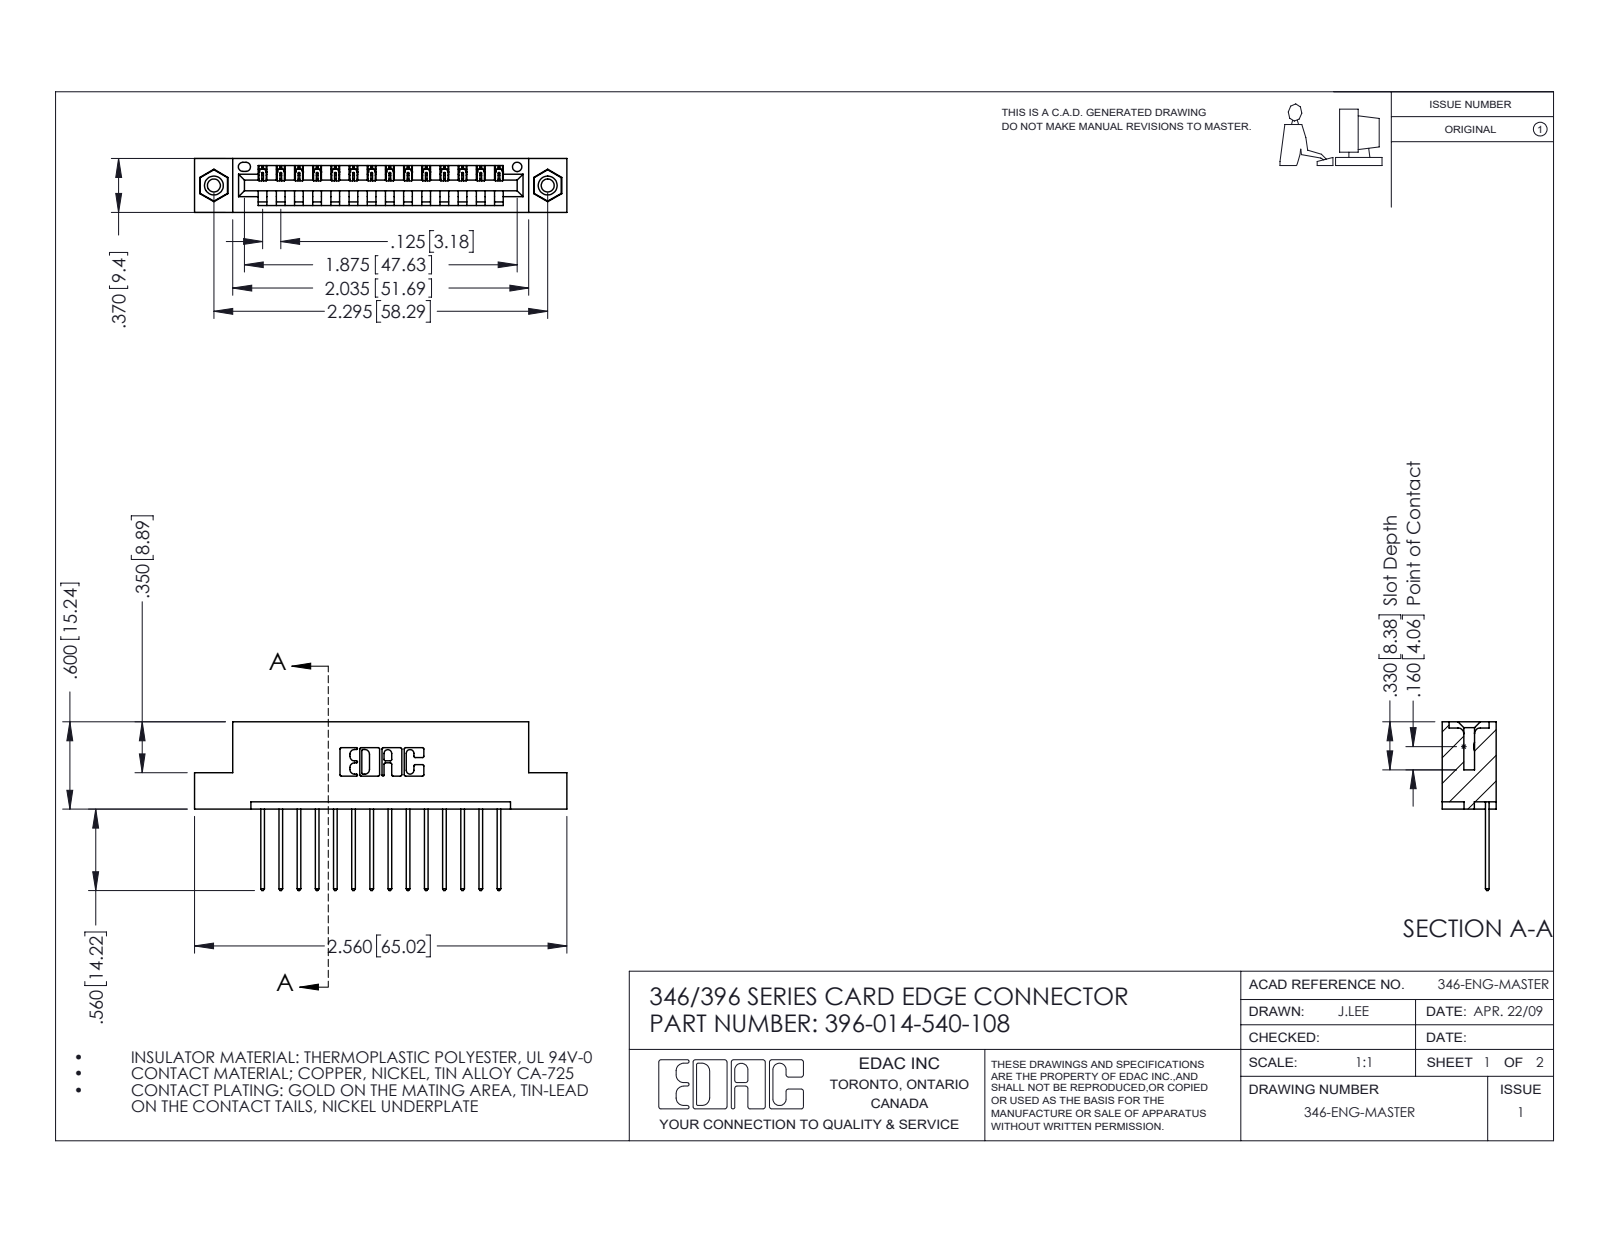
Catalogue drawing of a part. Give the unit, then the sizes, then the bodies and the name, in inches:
Units: inches
Overall size (bounding box): 2.56 × 1.16 × 0.37
Round holes (diameter × count): ⌀0.089 ×2, ⌀0.125 ×2, ⌀0.156 ×2, ⌀0.064 ×1
Round bosses / shafts (diameter × count): ⌀0.155 ×2
Partial cylindrical surfaces — rounded edges, fillets, slot ends (radius × count): R0.006 ×28, R0.01 ×28, R0.01 ×22, R0.007 ×6, R0.031 ×6, R0.026 ×3, R0.031 ×2, R0.04 ×2
Main face-to-face distances: 0.048, 0.322, 0.25, 0.37, 0.072, 0.298, 0.025, 0.148, 0.222, 0.1
Hole centre spacings: 0.246, 2.089, 2.295
Volume: 0.369 in³ · Surface area: 11.49 in²
Bodies: 17 solids, 994 faces (668 planar, 310 cylindrical, 16 other)
Part name (STEP PRODUCT): 345-250-001_345-250-003-102; 396-014-540-108; 345-292-001_345-293-140; 346 Part_Flush Mounting Lugs - 0.156 Dia-TI
STEP written by: SolidWorks 2016 (CONFIG_CONTROL_DESIGN)
